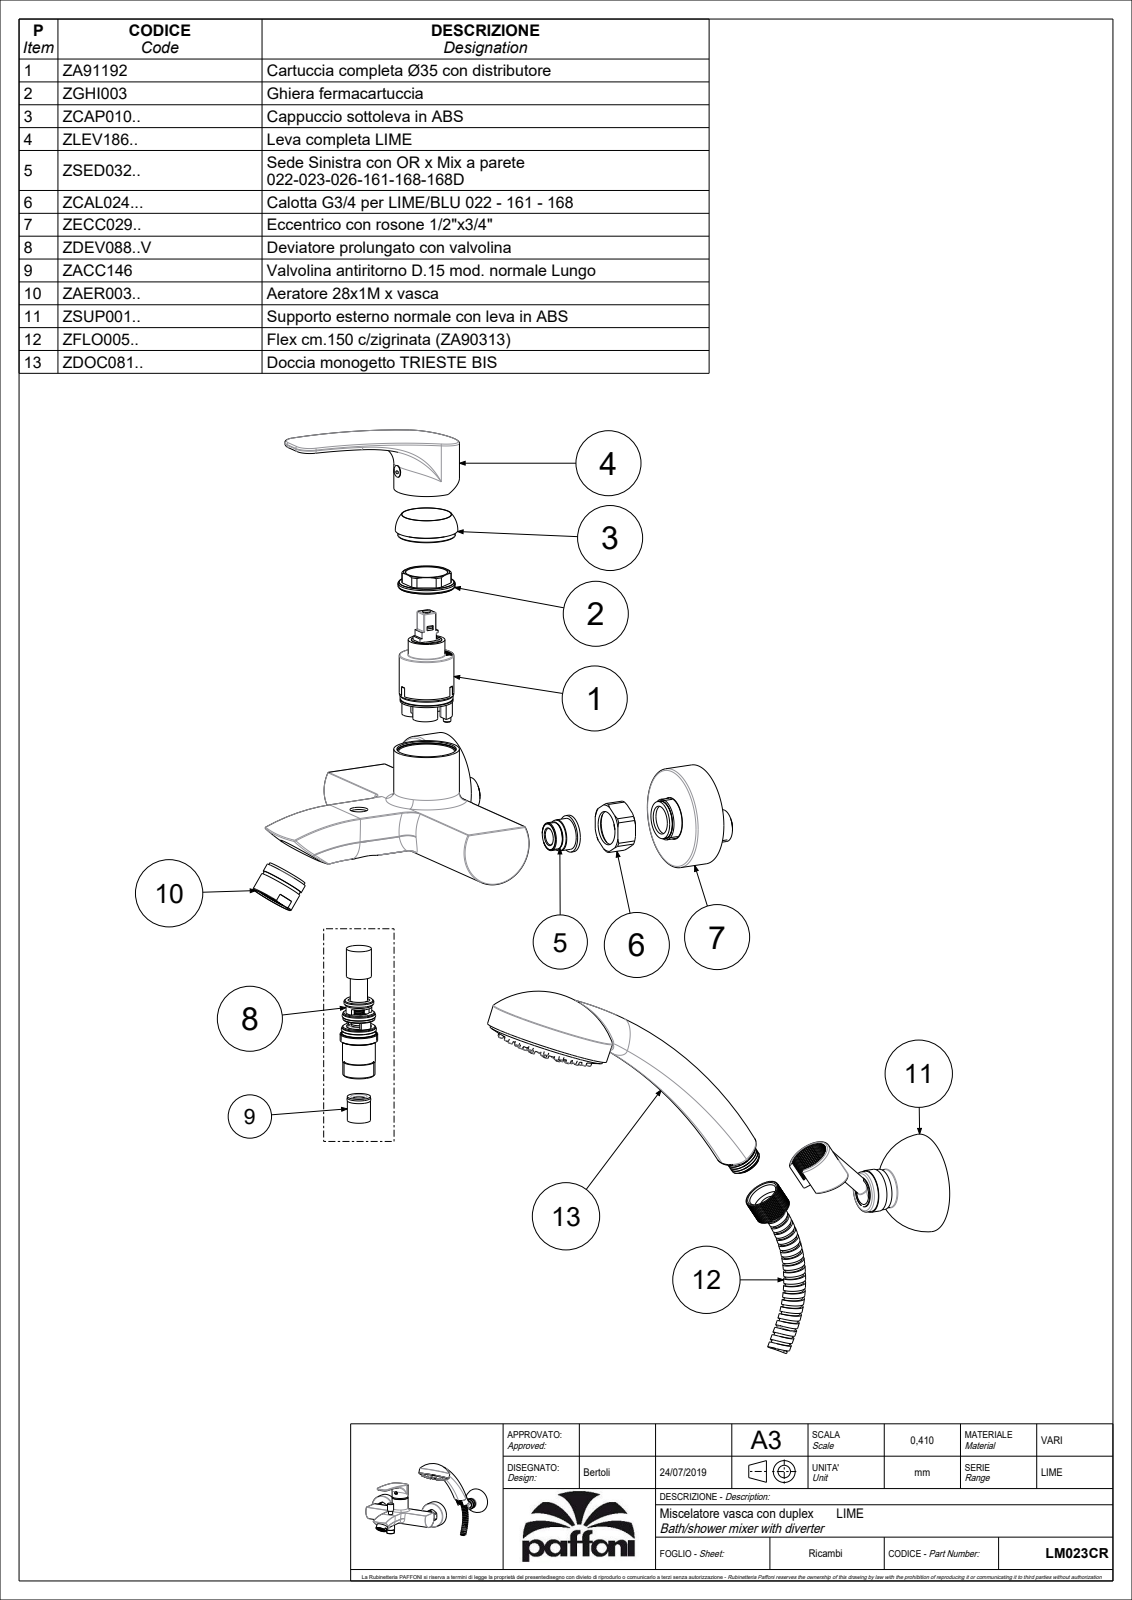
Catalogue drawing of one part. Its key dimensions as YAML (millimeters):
part_name: "LM023CR"
step_written_by: "CREO PARAMETRIC BY PTC INC, 2020044 (CONFIG_CONTROL_DESIGN)"
units: millimeters
bodies: {solids: 0, faces: 1832, planar: 865, cylindrical: 553, other: 414}
overall_size: [345.5, 271.95, 214.12]
round_holes:
  - {diameter: 1.5, count: 32}
  - {diameter: 12, count: 5}
  - {diameter: 9, count: 3}
  - {diameter: 18, count: 3}
  - {diameter: 7, count: 2}
  - {diameter: 8, count: 2}
  - {diameter: 9.5, count: 2}
  - {diameter: 10, count: 2}
  - {diameter: 16.3, count: 2}
  - {diameter: 19, count: 2}
  - {diameter: 20, count: 2}
  - {diameter: 62.3, count: 2}
round_bosses_or_shafts:
  - {diameter: 3, count: 48}
  - {diameter: 27, count: 3}
  - {diameter: 20.8, count: 3}
  - {diameter: 63.5, count: 2}
  - {diameter: 42, count: 2}
  - {diameter: 28, count: 2}
  - {diameter: 26.2, count: 2}
  - {diameter: 26, count: 2}
partial_cylinders:
  - {radius: 0.5, count: 42}
  - {radius: 1, count: 17}
  - {radius: 0.75, count: 16}
  - {radius: 0.3, count: 13}
  - {radius: 6, count: 4}
  - {radius: 7.25, count: 3}
  - {radius: 10, count: 3}
  - {radius: 4.5, count: 2}
face_to_face_distances: [2.5, 0.6, 110, 67.5, 88.75, 177.5, 65, 21.25, 3.5, 15.62]
hole_center_spacings: [31, 41.19, 51.04, 10.54, 14.11, 33.52, 37.44, 37.74]
